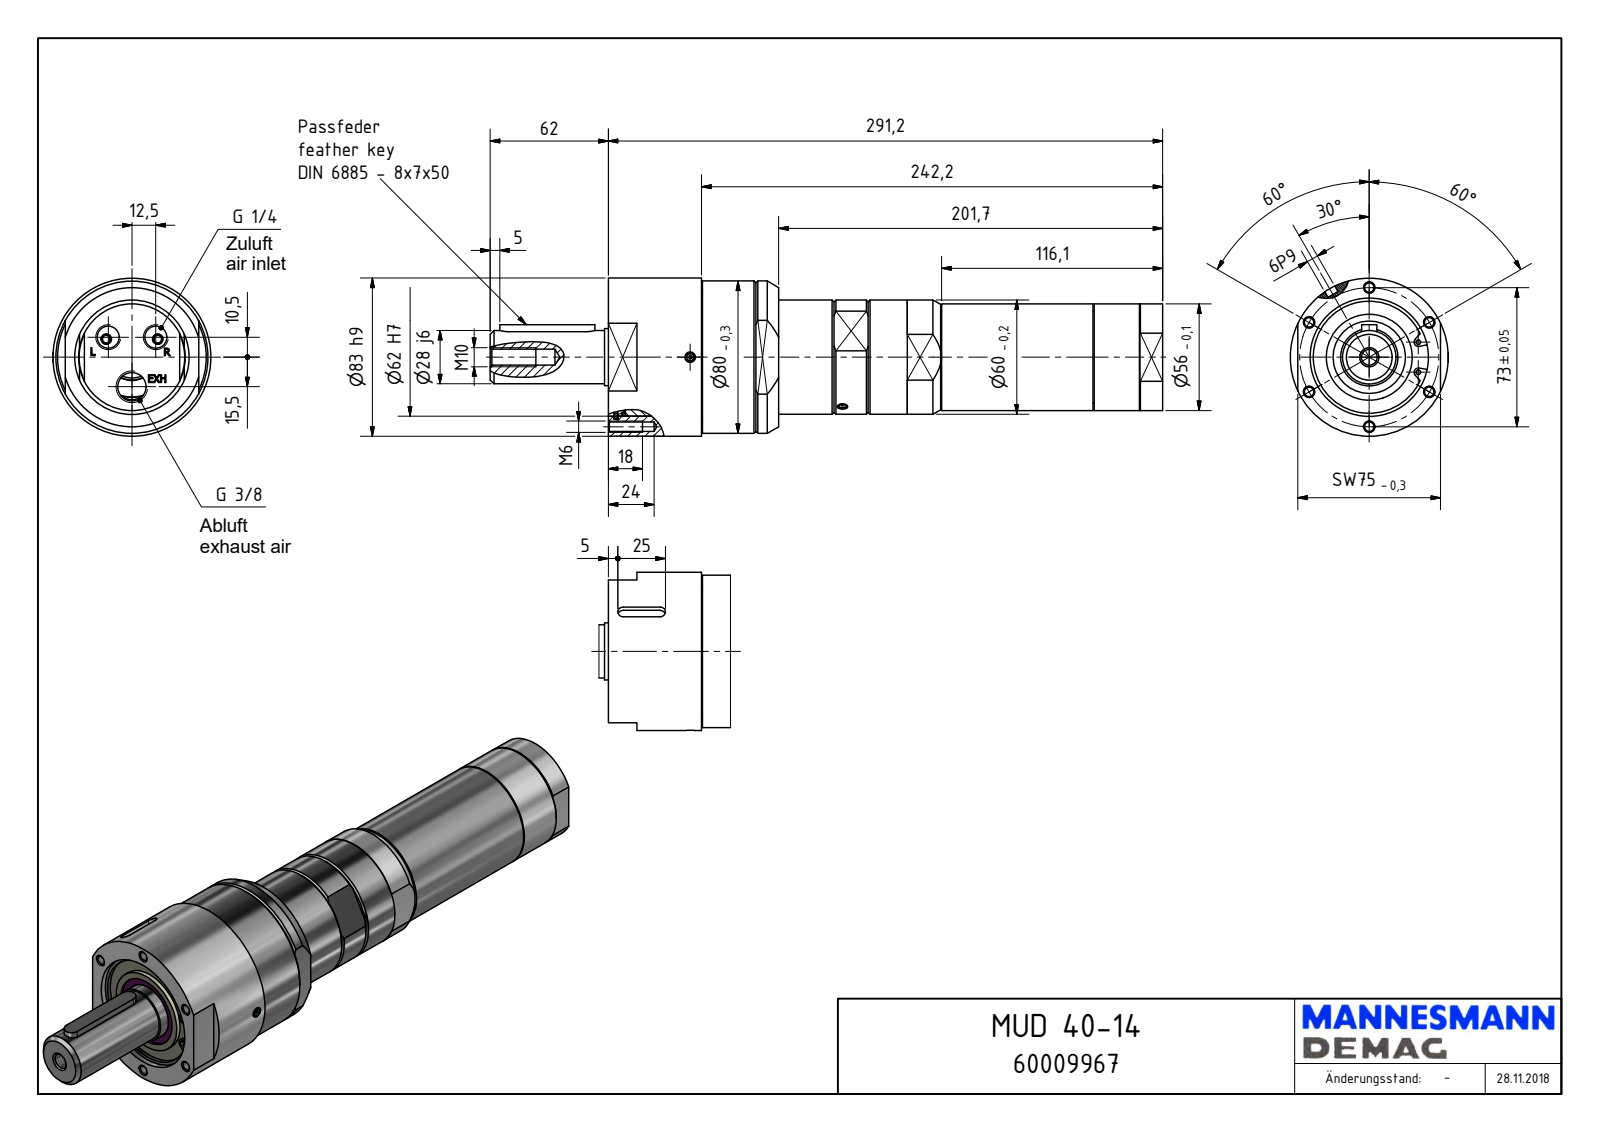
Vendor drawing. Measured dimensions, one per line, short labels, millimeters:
name: MUD 40-14_60009967
written by: Autodesk Inventor 2018 (AUTOMOTIVE_DESIGN)
unit: mm
bodies: 1 solid, 302 faces (146 planar, 87 cylindrical, 69 other)
size: 353.2 × 83 × 83
volume: 1 001 000 mm³; area: 95 763 mm²
holes: 6× ⌀4.92, 2× ⌀1.55, 2× ⌀2.5, 2× ⌀4, 2× ⌀5.5, 2× ⌀11.45, 1× ⌀8.38, 1× ⌀14.95, 1× ⌀36.5, 1× ⌀38, 1× ⌀40, 1× ⌀48.38
bosses: 2× ⌀5, 2× ⌀3.6, 1× ⌀83, 1× ⌀80, 1× ⌀68.18, 1× ⌀67, 1× ⌀60, 1× ⌀56
rounds: 2× R2.25, 2× R3, 2× R4, 2× R6, 1× R19.98, 1× R23, 1× R25.1, 1× R32.5
face distances: 2.5, 291.2, 49, 242.2, 0.5, 10, 62.5, 89.5, 40.5, 201.7
hole spacings: 36.5, 63.22, 28.85, 73, 11.89, 16.32, 20.62, 26.77
